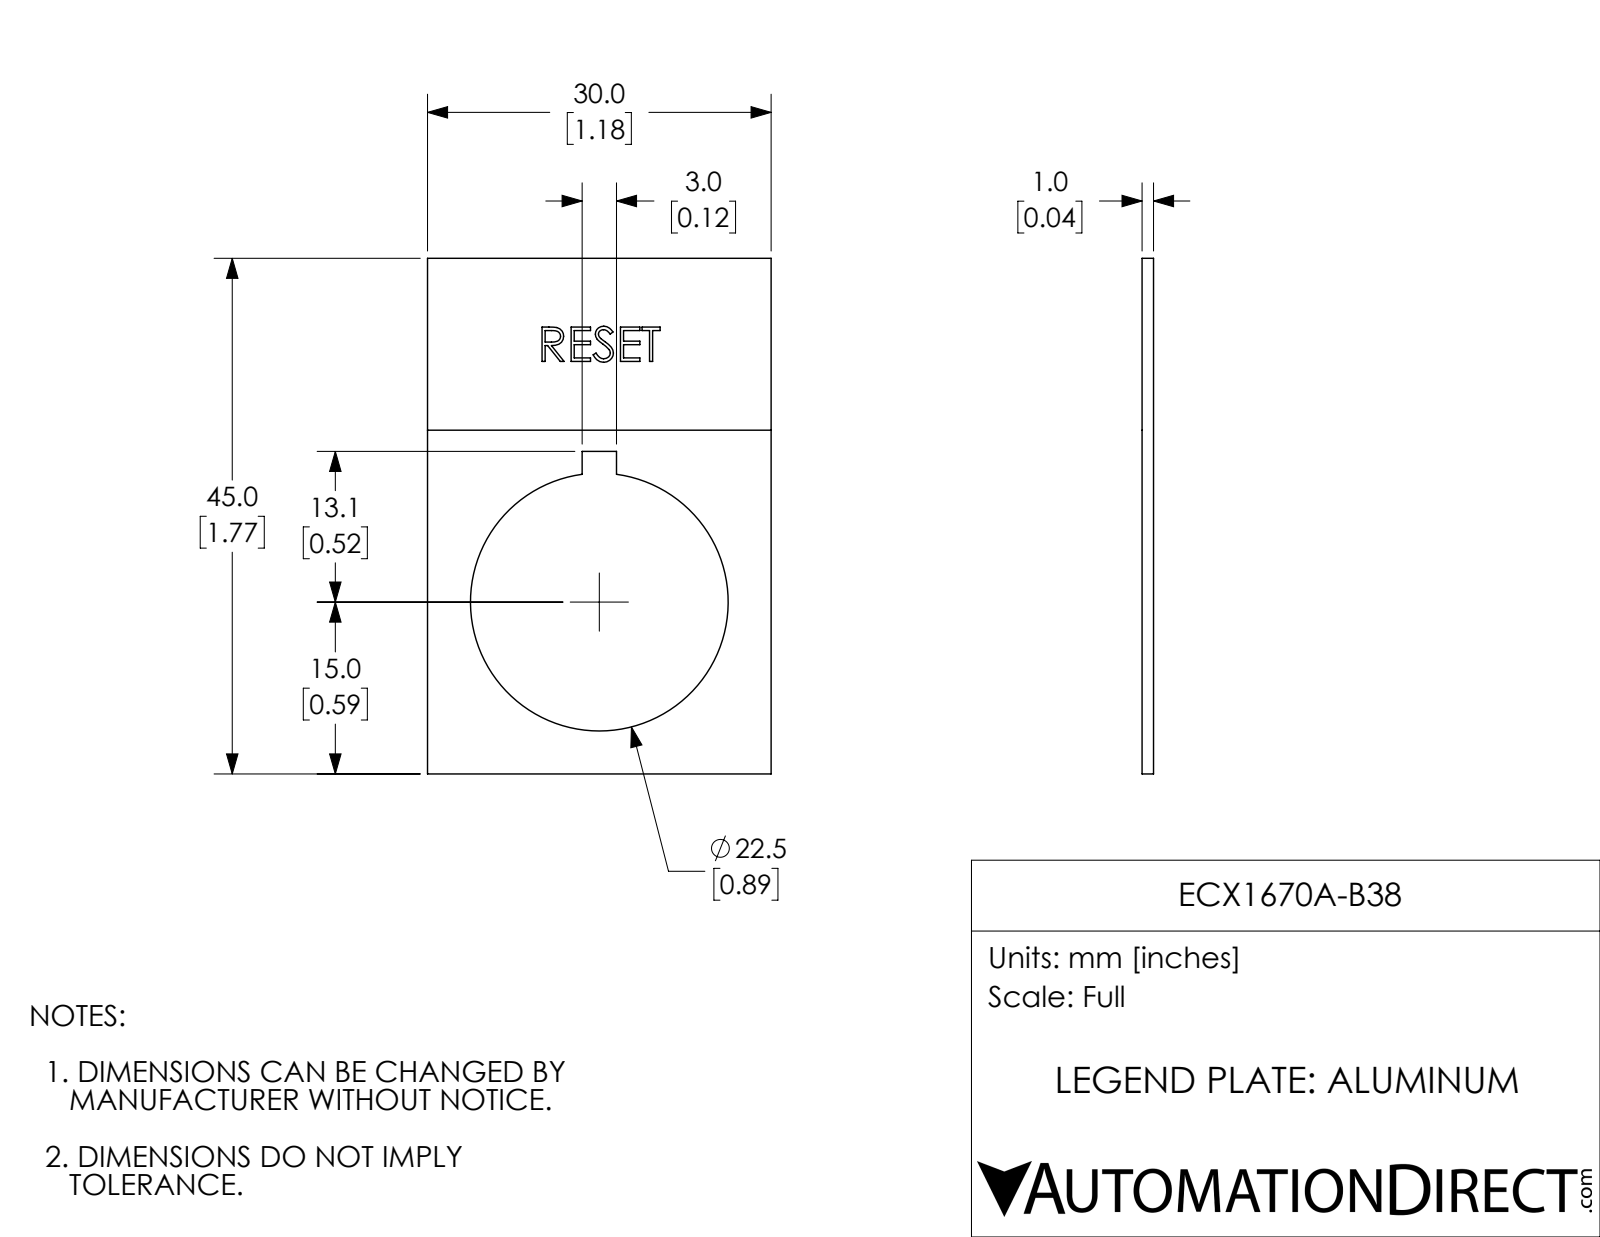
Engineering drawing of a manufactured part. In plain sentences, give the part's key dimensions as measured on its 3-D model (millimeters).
The part is named "ECX1670A-B38". Its 3-D file was written by "SolidWorks 2017 (AUTOMOTIVE_DESIGN)". It is 1 solid with 84 faces: 61 planar, 3 cylindrical and 20 other. Overall it measures 45 by 30 by 1 millimeters. Its volume is 950 cubic millimeters and its surface area 2 119 square millimeters. Round holes: 1 of diameter 22.5. The main face-to-face distances are 1, 30, 45, 1, 13.5, 16.5, 16.8, 28.1, 3, 0.3.
